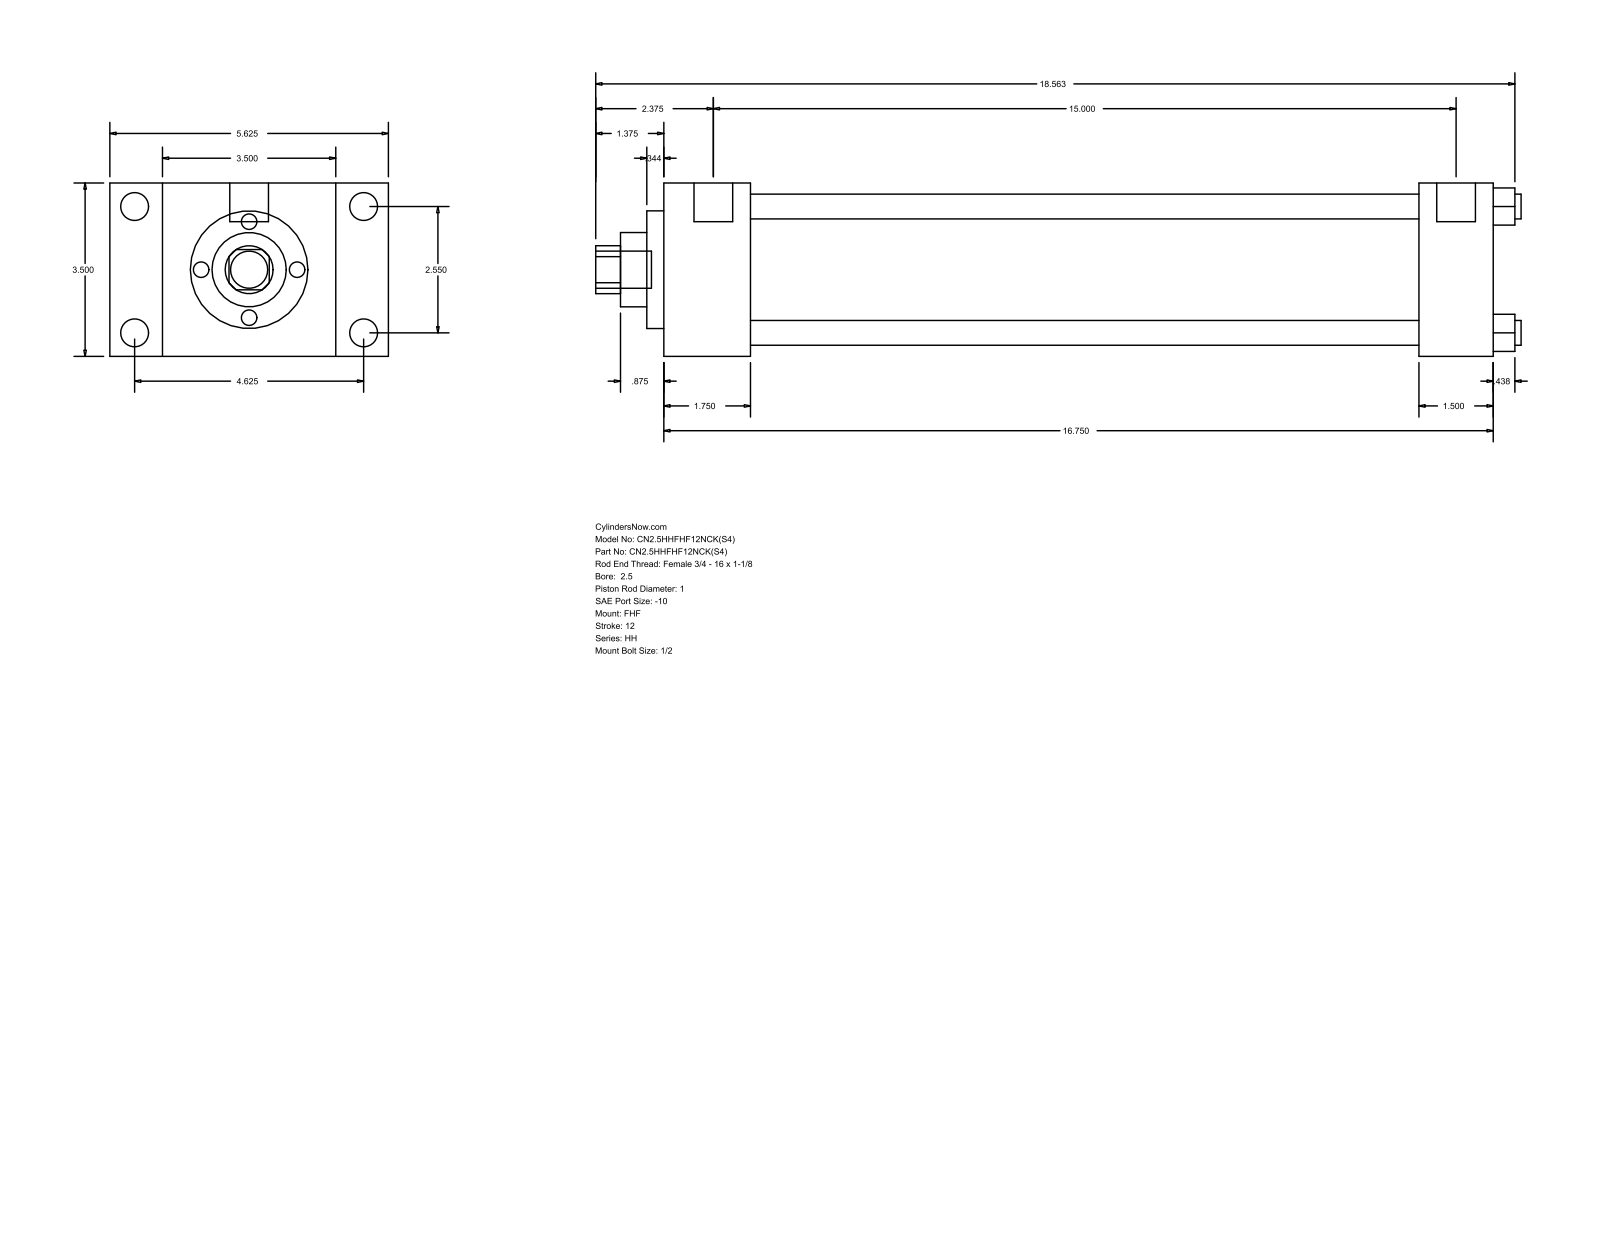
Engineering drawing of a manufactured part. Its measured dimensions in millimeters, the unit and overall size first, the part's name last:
Units: millimetres
Overall size (bounding box): 474.66 × 142.88 × 88.9
Round holes (diameter × count): ⌀12.7 ×4, ⌀25.4 ×1, ⌀38.1 ×1, ⌀60.33 ×1, ⌀73.03 ×1
Round bosses / shafts (diameter × count): ⌀14.3 ×4, ⌀5.56 ×4, ⌀19.84 ×2, ⌀19.05 ×1
Partial cylindrical surfaces — rounded edges, fillets, slot ends (radius × count): R12.29 ×1
Main face-to-face distances: 88.9, 44.46, 26.99, 115.89, 425.46, 381, 142.88, 387.35, 342.89, 38.11
Hole centre spacings: 45.79, 64.76, 91.58
Bodies: 0 solids, 90 faces (61 planar, 29 cylindrical, 0 other)
Part name (STEP PRODUCT): HH_FHF__0250_1
STEP written by: GSSL Pune (CONFIG_CONTROL_DESIGN)
